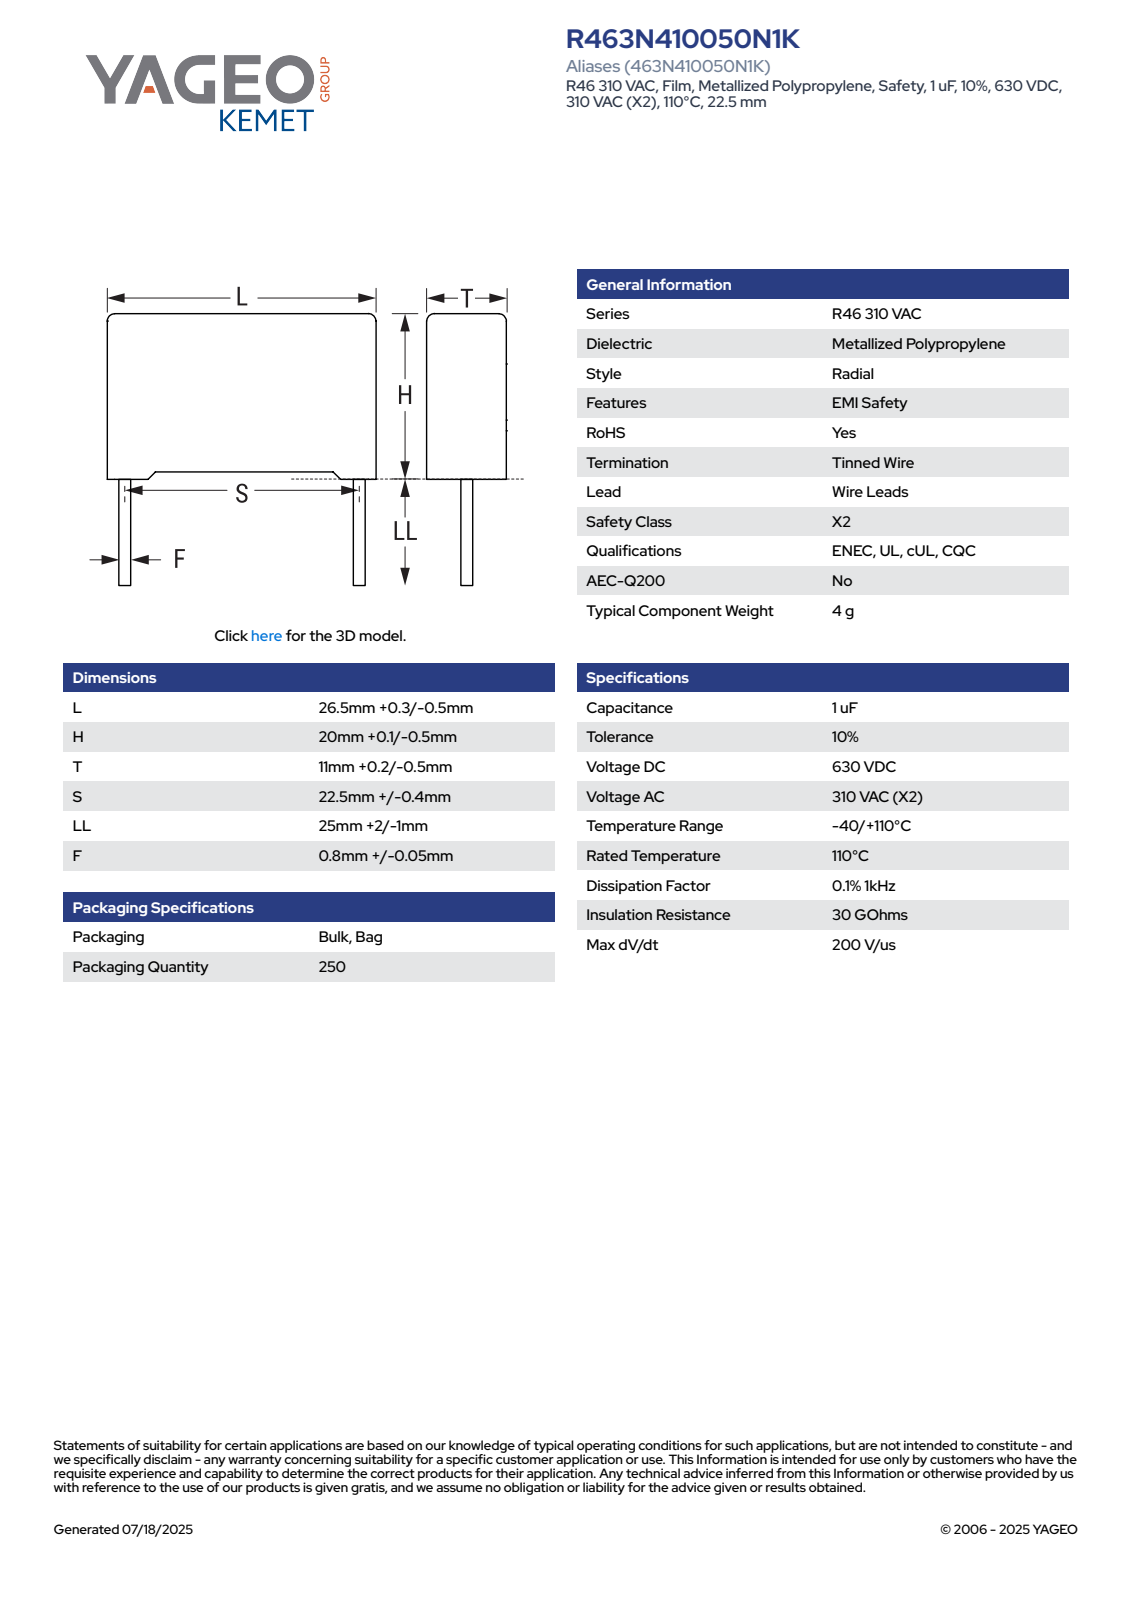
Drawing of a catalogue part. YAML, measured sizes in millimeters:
part_name: "CFR_RB2_26.5X20X11_L26.8H20.1T11.2S22.5LL27F0.85"
step_written_by: "SolidWorks 2021 (AUTOMOTIVE_DESIGN)"
units: millimeters
bodies: {solids: 4, faces: 85, planar: 77, cylindrical: 8, other: 0}
overall_size: [47.1, 26.8, 11.21]
volume: 5861
surface_area: 2314
round_bosses_or_shafts:
  - {diameter: 0.85, count: 2}
partial_cylinders:
  - {radius: 0.5, count: 4}
face_to_face_distances: [11.2, 19.35, 26.8, 19.41, 0.75, 0.69, 20.1, 0.89, 25.91, 11.21]
